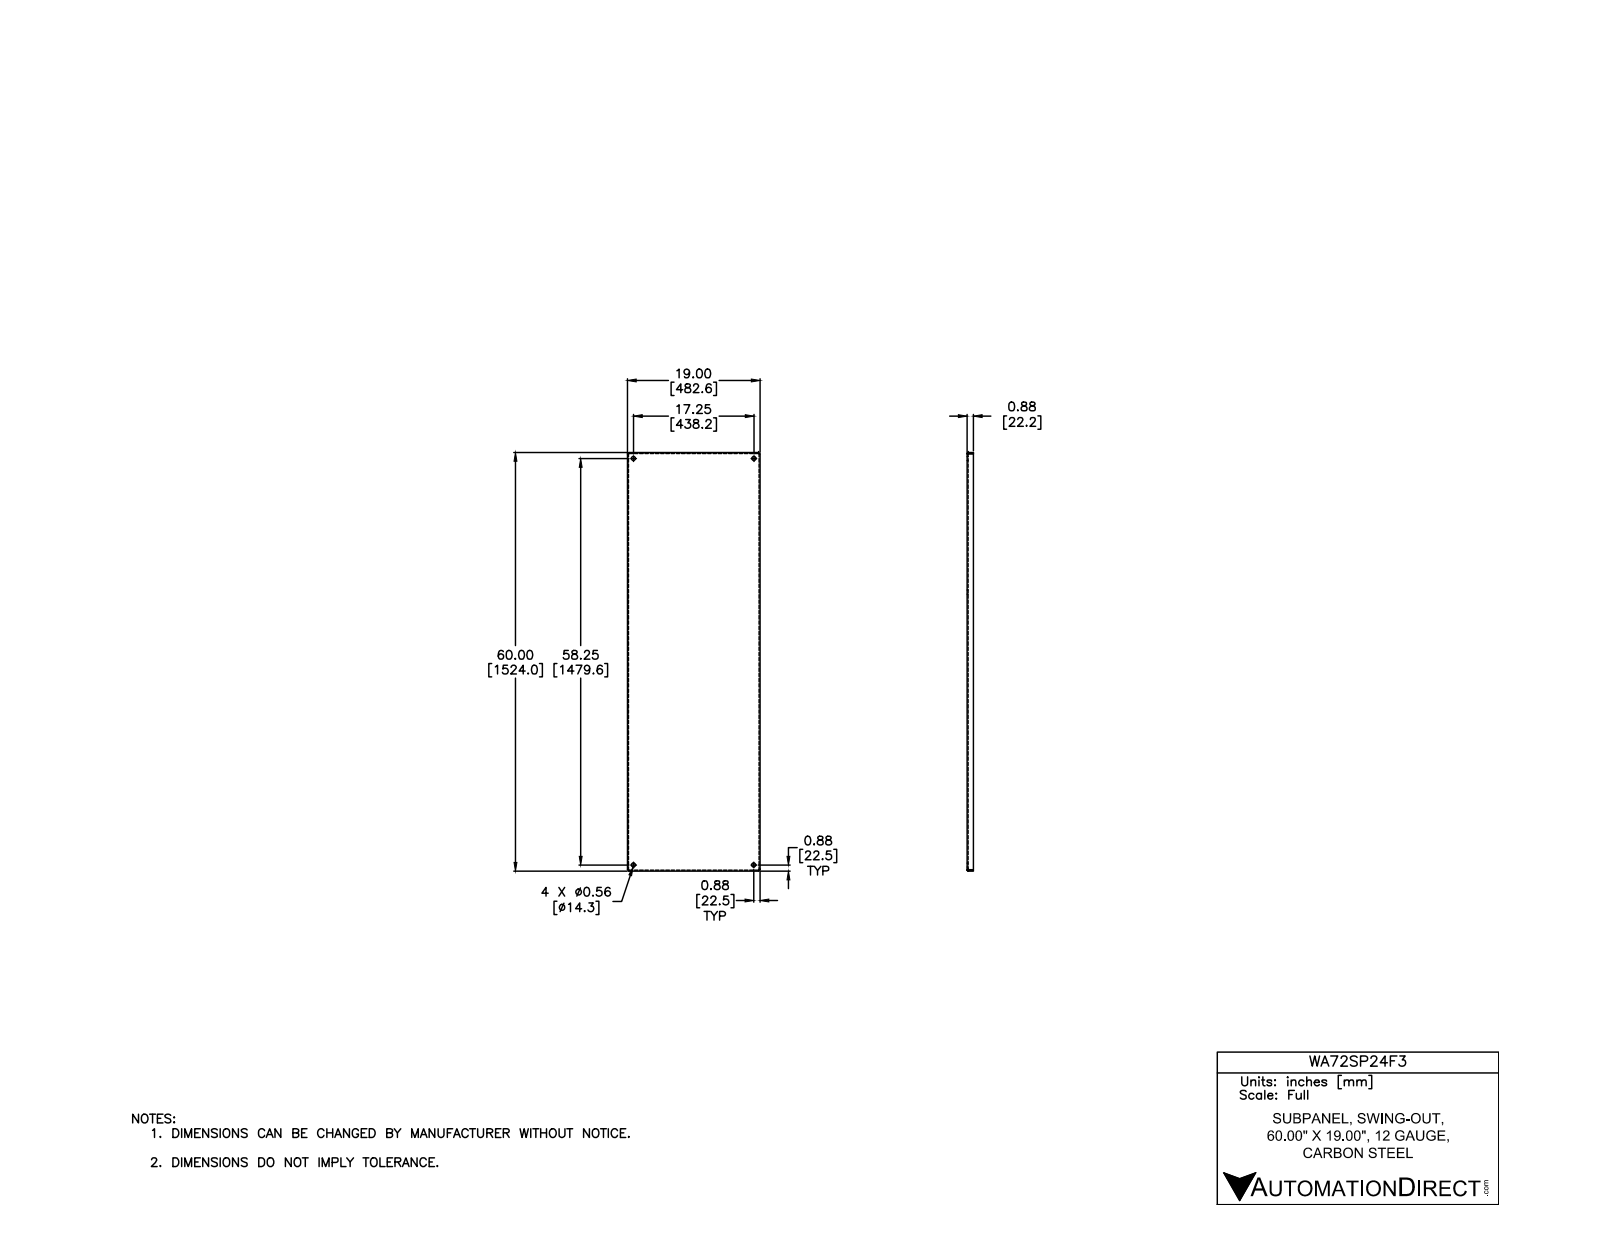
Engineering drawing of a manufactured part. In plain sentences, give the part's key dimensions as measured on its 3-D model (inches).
The part is named "WA60SP24F3-WA90SP36F4". Its 3-D file was written by "Autodesk Inventor 2012 (AUTOMOTIVE_DESIGN)". It is 1 solid with 42 faces: 22 planar, 12 cylindrical and 8 other. Overall it measures 60 by 19 by 0.875 inches. Its volume is 117.8 cubic inches and its surface area 2 528 square inches. Round holes: 4 of diameter 0.563. Partial cylindrical surfaces (rounded edges, fillets, slot ends): 4 of radius 0.031, 4 of radius 0.125. The main face-to-face distances are 0.094, 18.906, 19, 18.813, 59.906, 0.781, 0.875, 60, 59.813, 0.16. The hole center spacings are 58.25, 17.25, 17.25, 60.75, 60.751.
